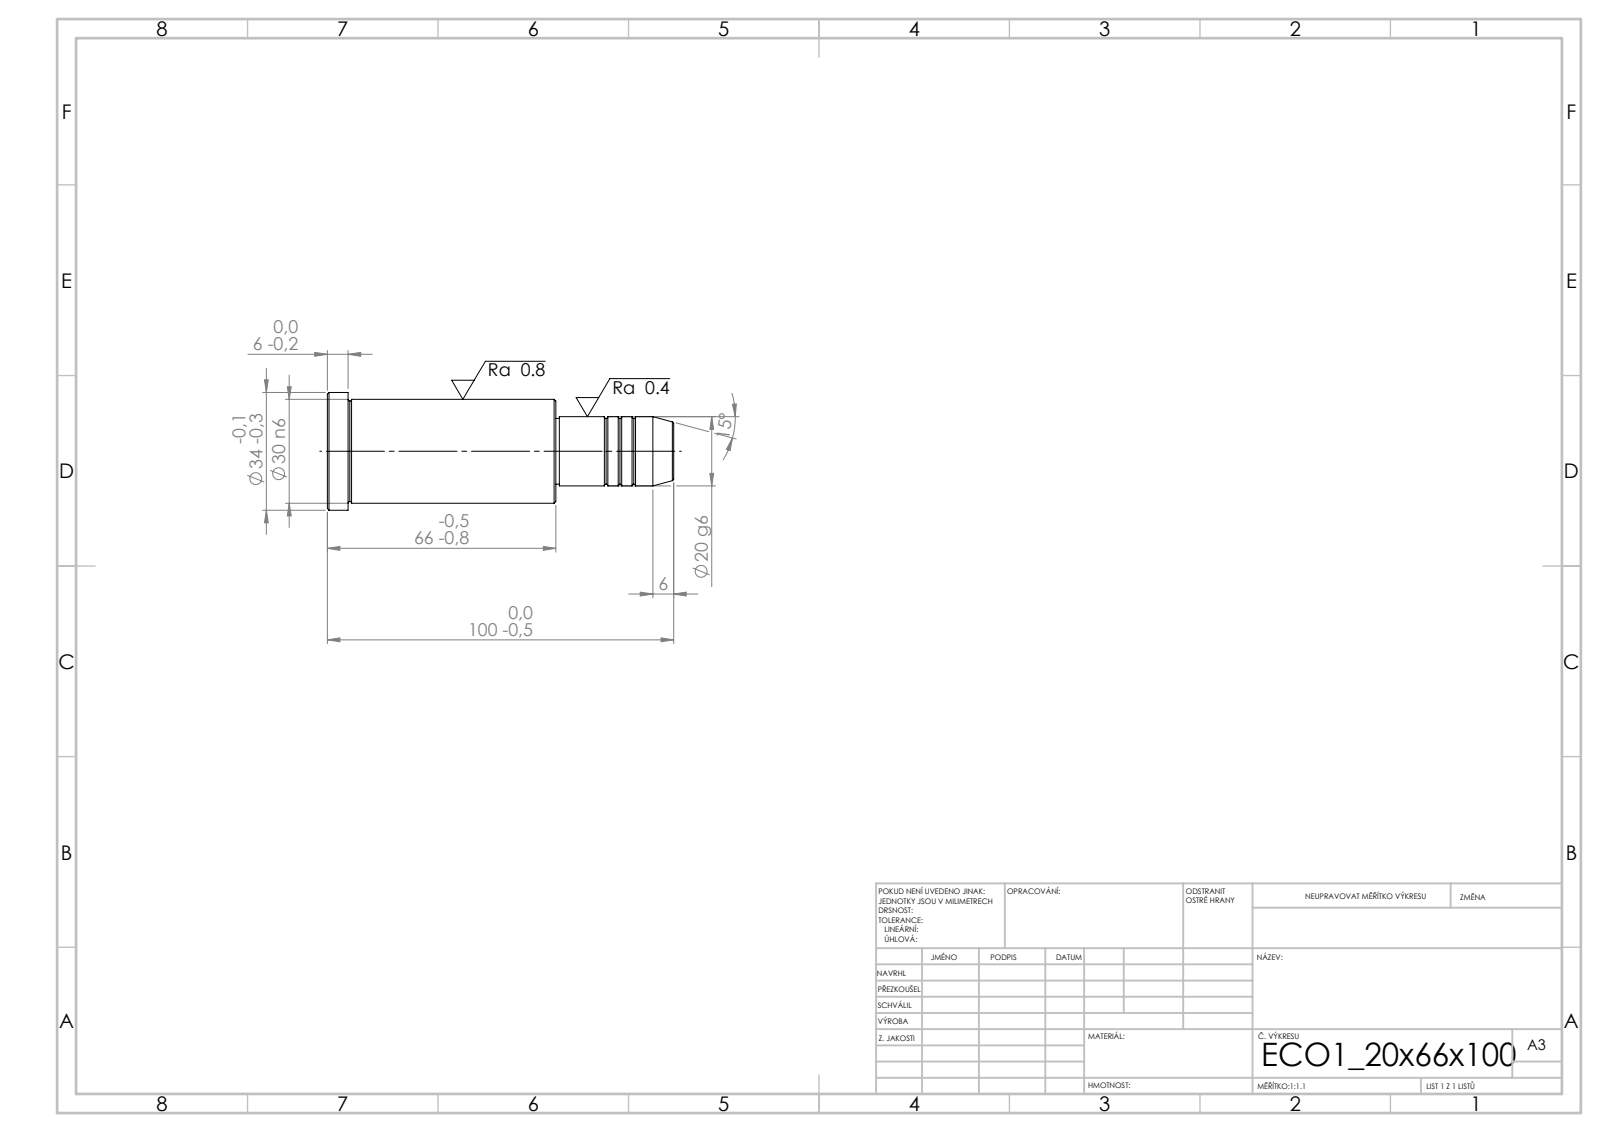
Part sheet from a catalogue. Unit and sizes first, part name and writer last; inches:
Units: inches
Overall size (bounding box): 3.937 × 1.339 × 1.339
Round bosses / shafts (diameter × count): ⌀1.339 ×1, ⌀1.181 ×1, ⌀0.787 ×1, ⌀0.748 ×1
Main face-to-face distances: 2.598, 1.339, 3.937, 3.701, 2.362, 0.236, 1.299, 0.039, 2.402, 2.638
Volume: 3.545 in³ · Surface area: 15.93 in²
Bodies: 1 solid, 43 faces (5 planar, 14 cylindrical, 24 other)
STEP written by: SolidWorks 2019 (CONFIG_CONTROL_DESIGN)
